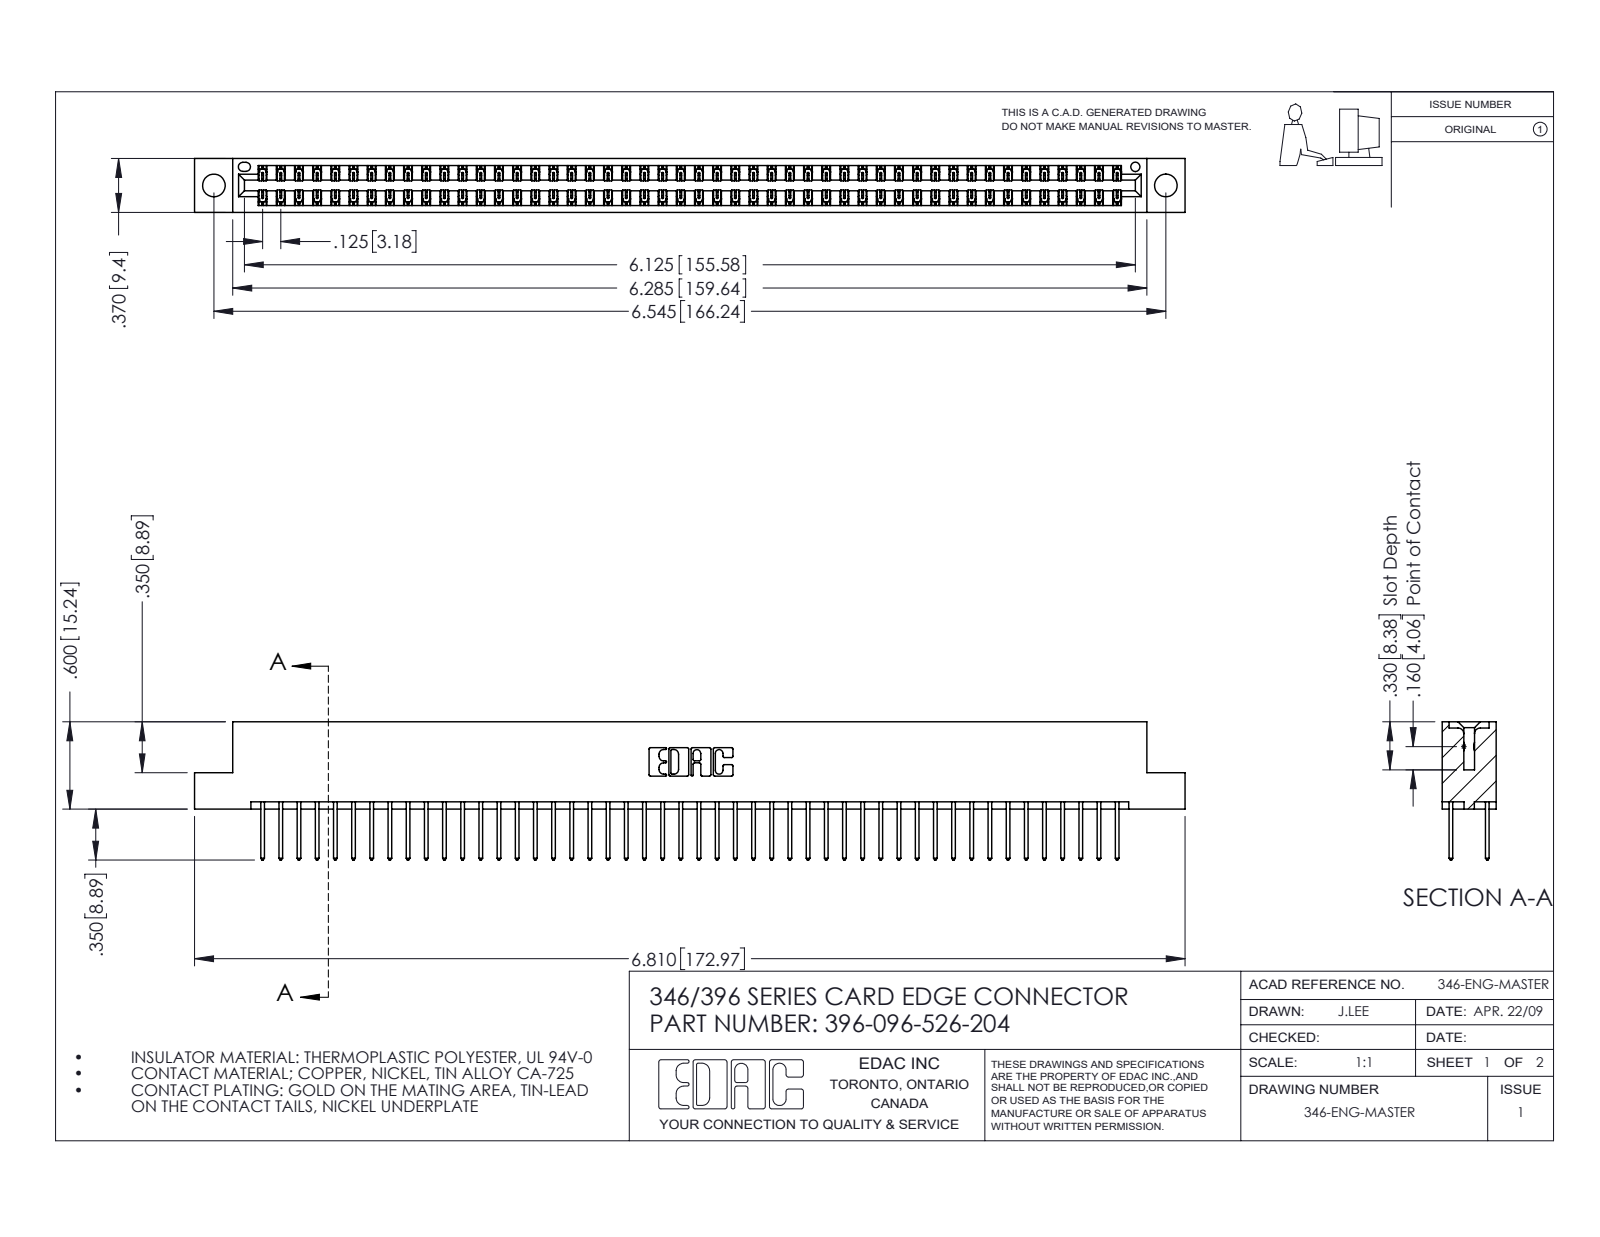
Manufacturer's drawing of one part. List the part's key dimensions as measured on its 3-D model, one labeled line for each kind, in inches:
Part name (STEP PRODUCT): 346 Part_Flush Mounting Lugs - 0.156 Dia-TH; 396-096-526-204; 345-292-001_345-293-126
STEP written by: SolidWorks 2016 (CONFIG_CONTROL_DESIGN)
Units: inches
Bodies: 97 solids, 5114 faces (3436 planar, 1678 cylindrical, 0 other)
Overall size (bounding box): 6.81 × 0.95 × 0.37
Volume: 1.036 in³ · Surface area: 37.13 in²
Round holes (diameter × count): ⌀0.156 ×2, ⌀0.064 ×1
Partial cylindrical surfaces — rounded edges, fillets, slot ends (radius × count): R0.006 ×144, R0.01 ×96, R0.01 ×22, R0.007 ×6, R0.031 ×6, R0.026 ×3, R0.014 ×2, R0.022 ×2
Main face-to-face distances: 0.048, 0.322, 0.25, 0.37, 0.072, 0.298, 0.025, 0.275, 0.148, 0.222
Hole centre spacings: 0.246, 6.336, 6.545
